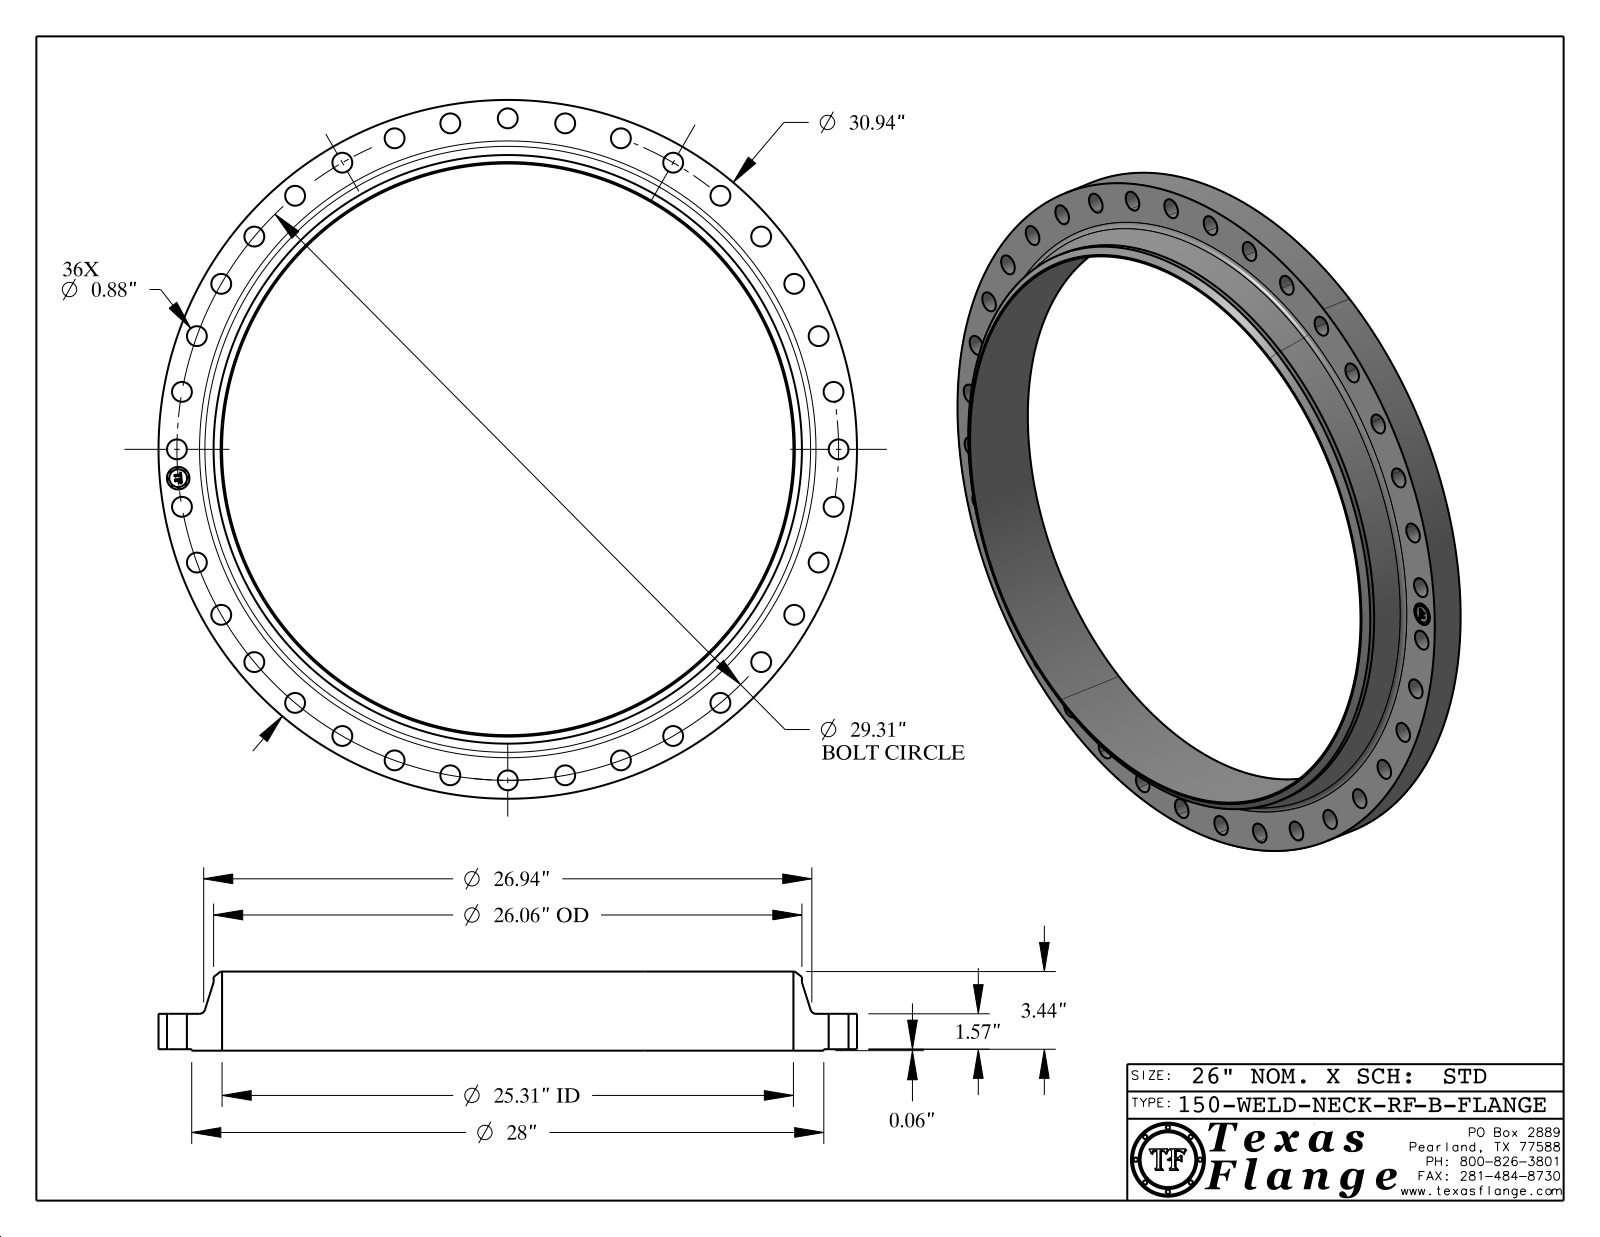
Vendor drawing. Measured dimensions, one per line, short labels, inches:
name: 150-WELD-NECK-RF, Series B
written by: CATIA V5 STEP AP214 (AUTOMOTIVE_DESIGN)
unit: in
bodies: 1 solid, 475 faces (369 planar, 100 cylindrical, 6 other)
size: 30.94 × 30.94 × 3.503
volume: 442.7 in³; area: 1 154 in²
holes: 36× ⌀0.88, 1× ⌀1, 1× ⌀25.31
bosses: 8× ⌀0.061, 1× ⌀30.94, 1× ⌀28, 1× ⌀26.06, 1× ⌀0.788
face distances: 1.57, 0.063, 1.633, 3.503, 3.44, 1.87, 1.618, 1.555, 0.015, 1.885
hole spacings: 14.655, 28.311, 12.387, 18.84, 24.009, 27.543, 29.198, 2.555
